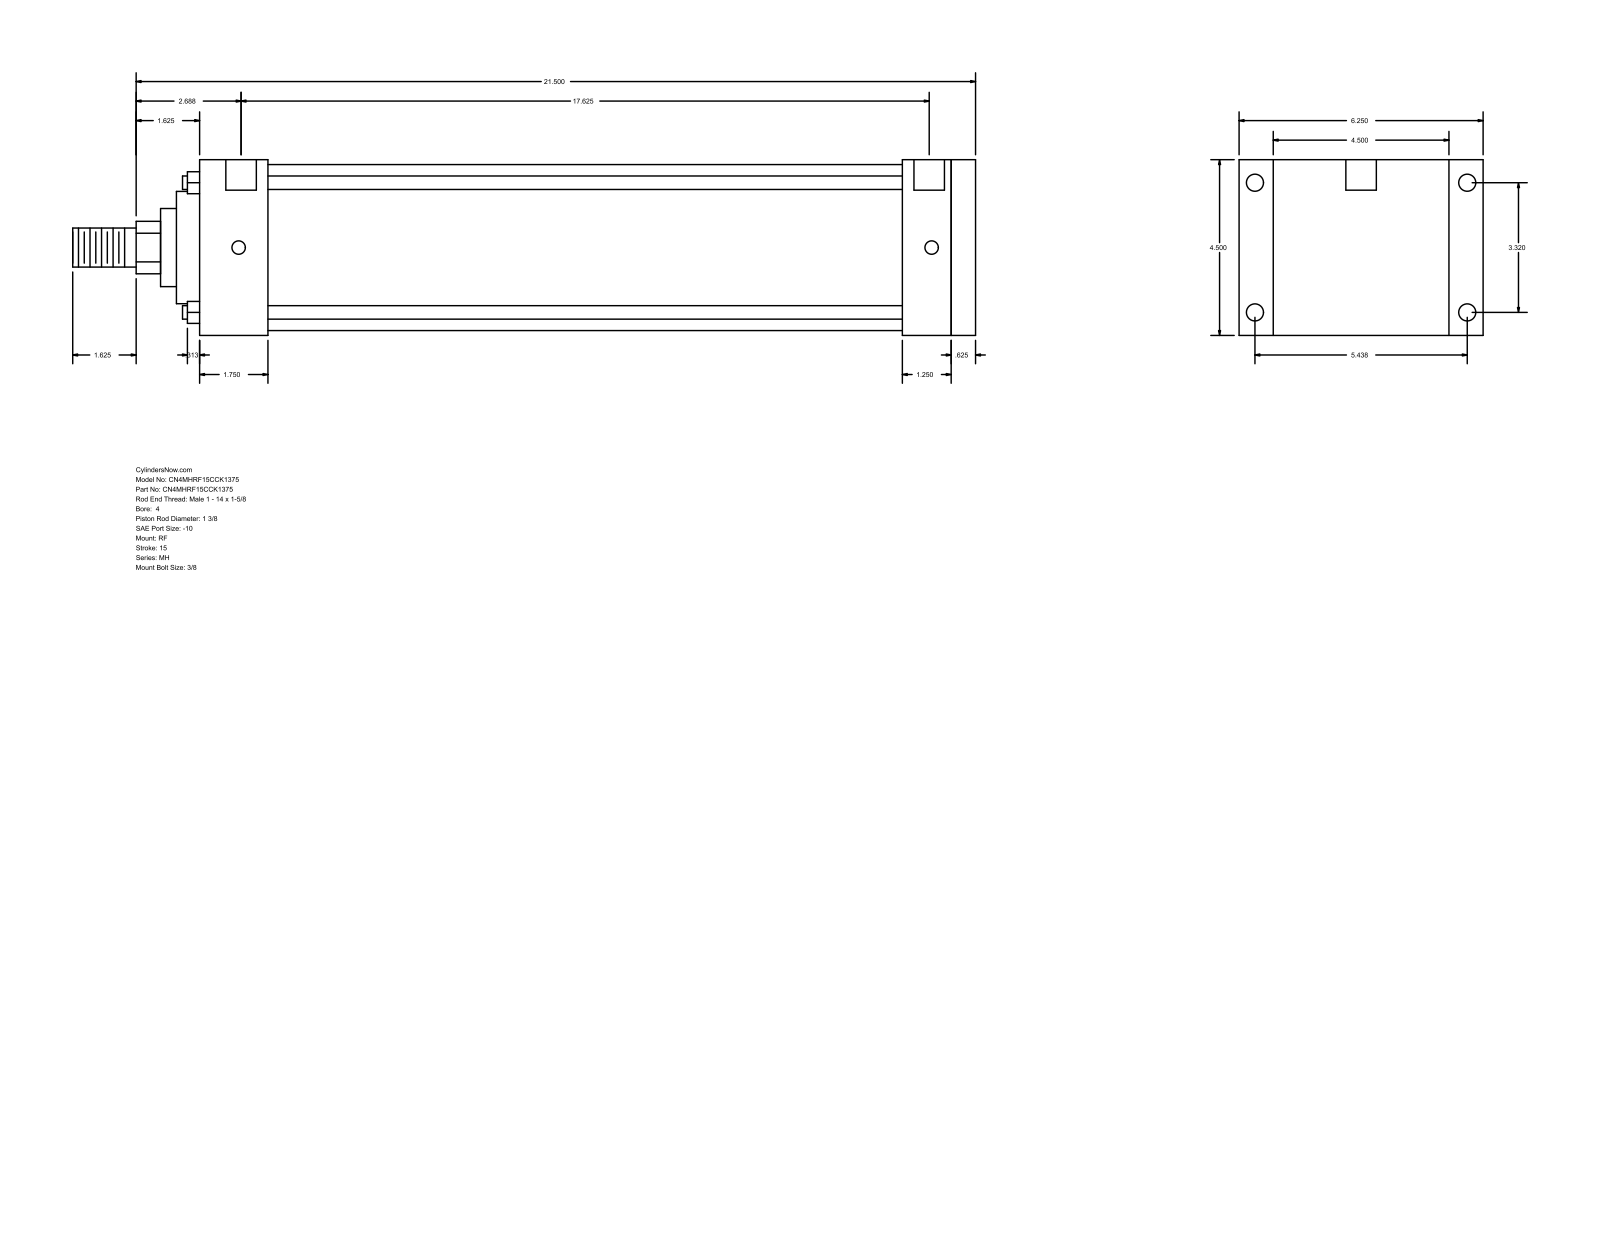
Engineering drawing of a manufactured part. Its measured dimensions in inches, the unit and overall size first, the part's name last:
Units: inches
Overall size (bounding box): 23.125 × 6.25 × 4.5
Round holes (diameter × count): ⌀0.344 ×4, ⌀0.438 ×4, ⌀0.781 ×2
Round bosses / shafts (diameter × count): ⌀0.345 ×4, ⌀4.25 ×1, ⌀2.875 ×1, ⌀2 ×1, ⌀1.375 ×1, ⌀1 ×1
Partial cylindrical surfaces — rounded edges, fillets, slot ends (radius × count): R0.672 ×1
Main face-to-face distances: 4.5, 19.875, 19.25, 0.625, 1.75, 17.5, 18.125, 18, 16.25, 1.25
Hole centre spacings: 3.32, 5.438, 6.371, 17.75, 0.062, 0.063, 17.625, 17.687
Bodies: 0 solids, 94 faces (65 planar, 29 cylindrical, 0 other)
Part name (STEP PRODUCT): MH_RF__0400_1.375
STEP written by: GSSL Pune (CONFIG_CONTROL_DESIGN)
